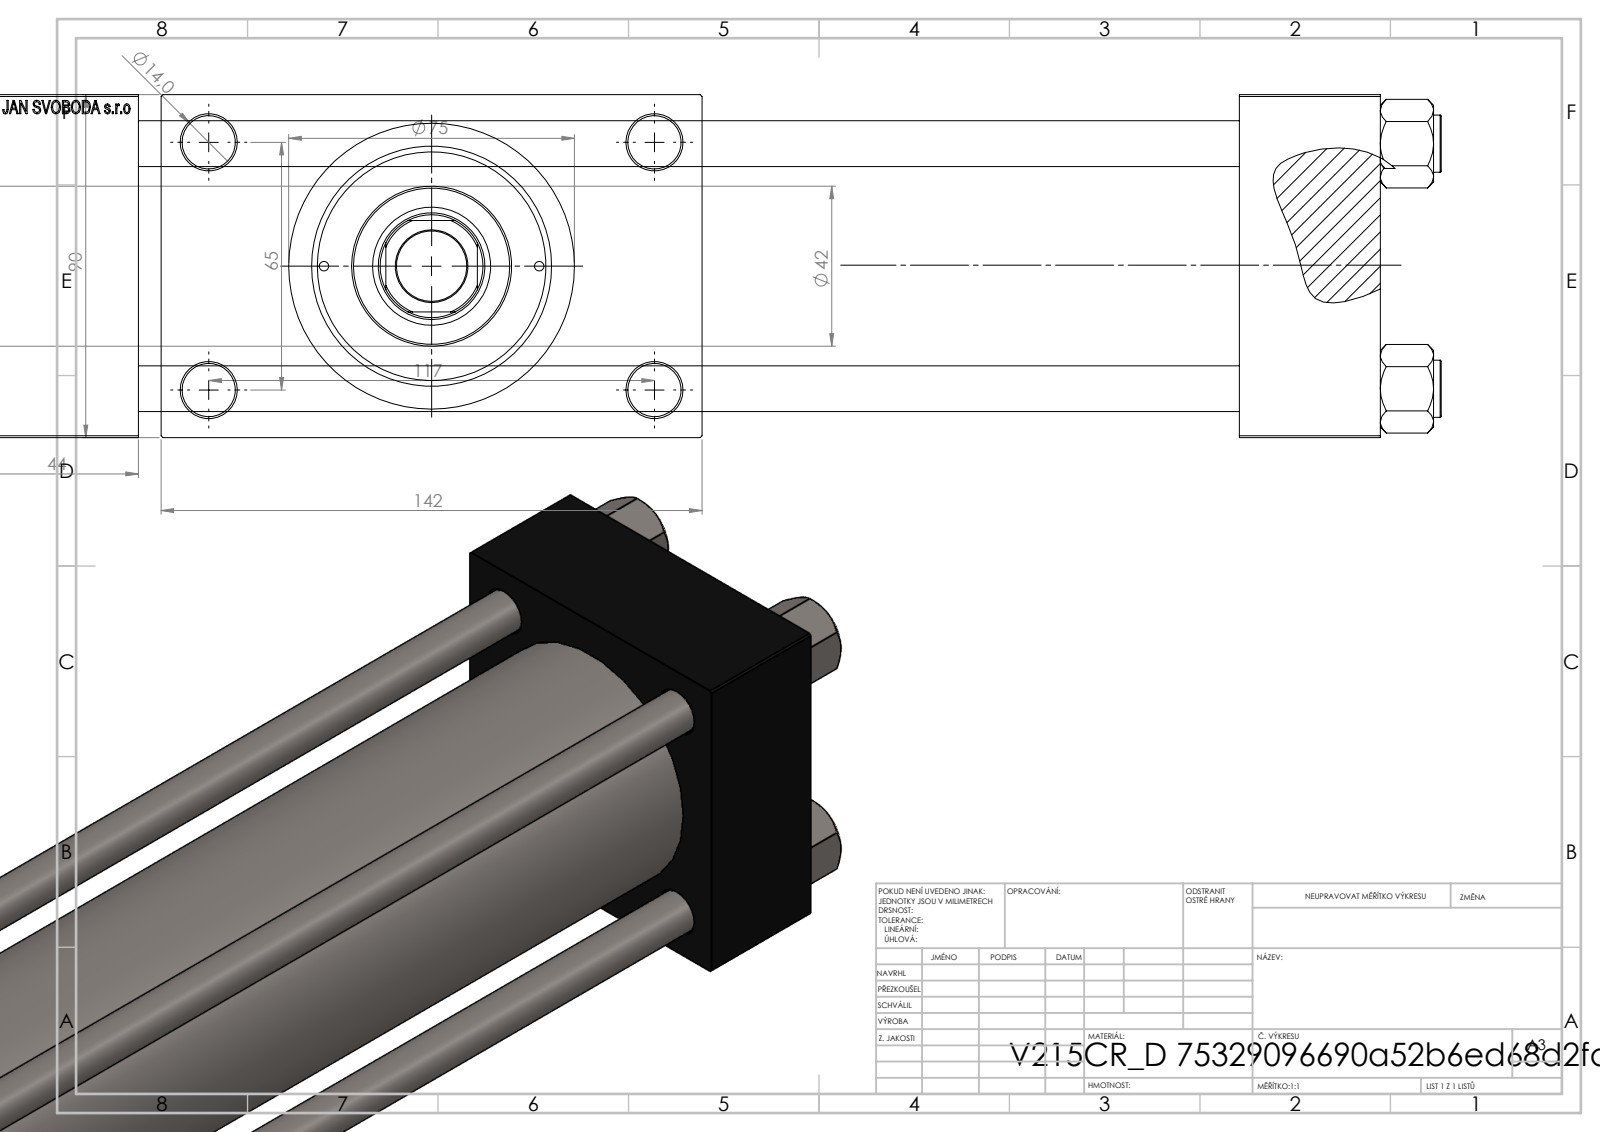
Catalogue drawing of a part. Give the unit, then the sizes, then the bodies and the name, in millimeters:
Units: millimetres
Overall size (bounding box): 433 × 142 × 90
Round holes (diameter × count): ⌀12 ×4, ⌀14 ×4, ⌀2.5 ×2, ⌀7 ×2, ⌀20.96 ×2, ⌀30 ×2, ⌀18.5 ×1, ⌀28 ×1, ⌀31 ×1, ⌀50 ×1, ⌀60 ×1, ⌀63 ×1
Round bosses / shafts (diameter × count): ⌀15 ×4, ⌀75 ×1, ⌀69 ×1, ⌀42 ×1
Partial cylindrical surfaces — rounded edges, fillets, slot ends (radius × count): R13.5 ×1
Main face-to-face distances: 90, 289, 37, 326, 333, 370, 44, 26, 116, 16
Hole centre spacings: 26.35, 32.39, 44.4, 45.47, 64.3, 66.92, 68.42, 69.81
Volume: 1 485 000 mm³ · Surface area: 350 523 mm²
Bodies: 11 solids, 1111 faces (499 planar, 92 cylindrical, 520 other)
Part name (STEP PRODUCT): V215CR_VCP_D; V215CR_D_TYCINKA; V215CR_D_Body; V215_VC_A (+1 more)
STEP written by: SolidWorks 2019 (CONFIG_CONTROL_DESIGN)
